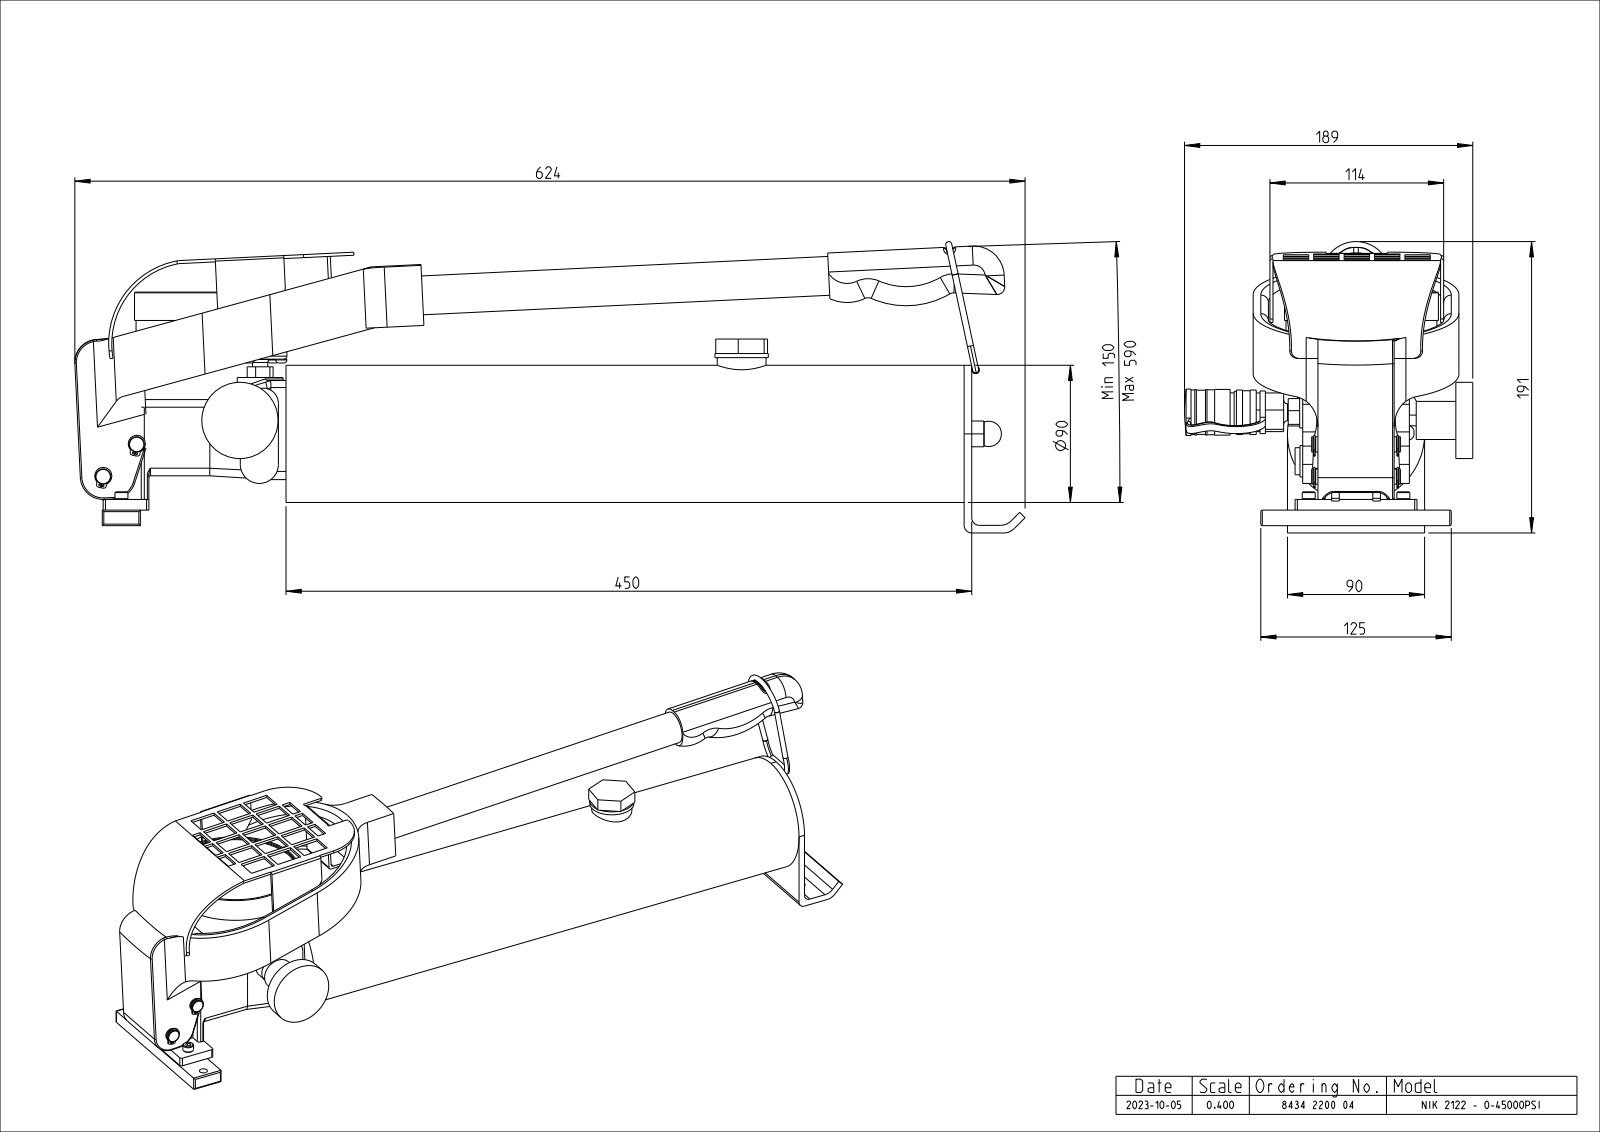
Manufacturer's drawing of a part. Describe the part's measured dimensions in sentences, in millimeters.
The part is named "pump tank (high pressure); suction pipe; grooved pin; piston spring (+8 more)". Its 3-D file was written by "SolidWorks 2022 (AUTOMOTIVE_DESIGN)". It is 56 solids with 1725 faces: 622 planar, 731 cylindrical and 372 other. Overall it measures 623.6 by 191.13 by 189.15 millimeters. Its volume is 1 812 000 cubic millimeters and its surface area 632 068 square millimeters. Round holes: 12 of diameter 4, 8 of diameter 1.2, 8 of diameter 5, 4 of diameter 6, 3 of diameter 5.5, 3 of diameter 8, 3 of diameter 10, 2 of diameter 3, 2 of diameter 6.4, 2 of diameter 6.9, 2 of diameter 7.5, 2 of diameter 7.8. Round bosses or shafts: 4 of diameter 8.5, 4 of diameter 7.3, 4 of diameter 4, 3 of diameter 9.8, 2 of diameter 31, 2 of diameter 30, 2 of diameter 25.5, 2 of diameter 20.6. Partial cylindrical surfaces (rounded edges, fillets, slot ends): 26 of radius 5, 23 of radius 1, 21 of radius 2, 20 of radius 0.5, 14 of radius 1.5, 10 of radius 15, 8 of radius 2.28, 7 of radius 10. The main face-to-face distances are 2, 5, 10, 32.5, 7, 443, 15, 50, 450, 42. The hole center spacings are 6.05, 6, 2.2, 9, 12.73, 96.15, 1.05, 7.52.
